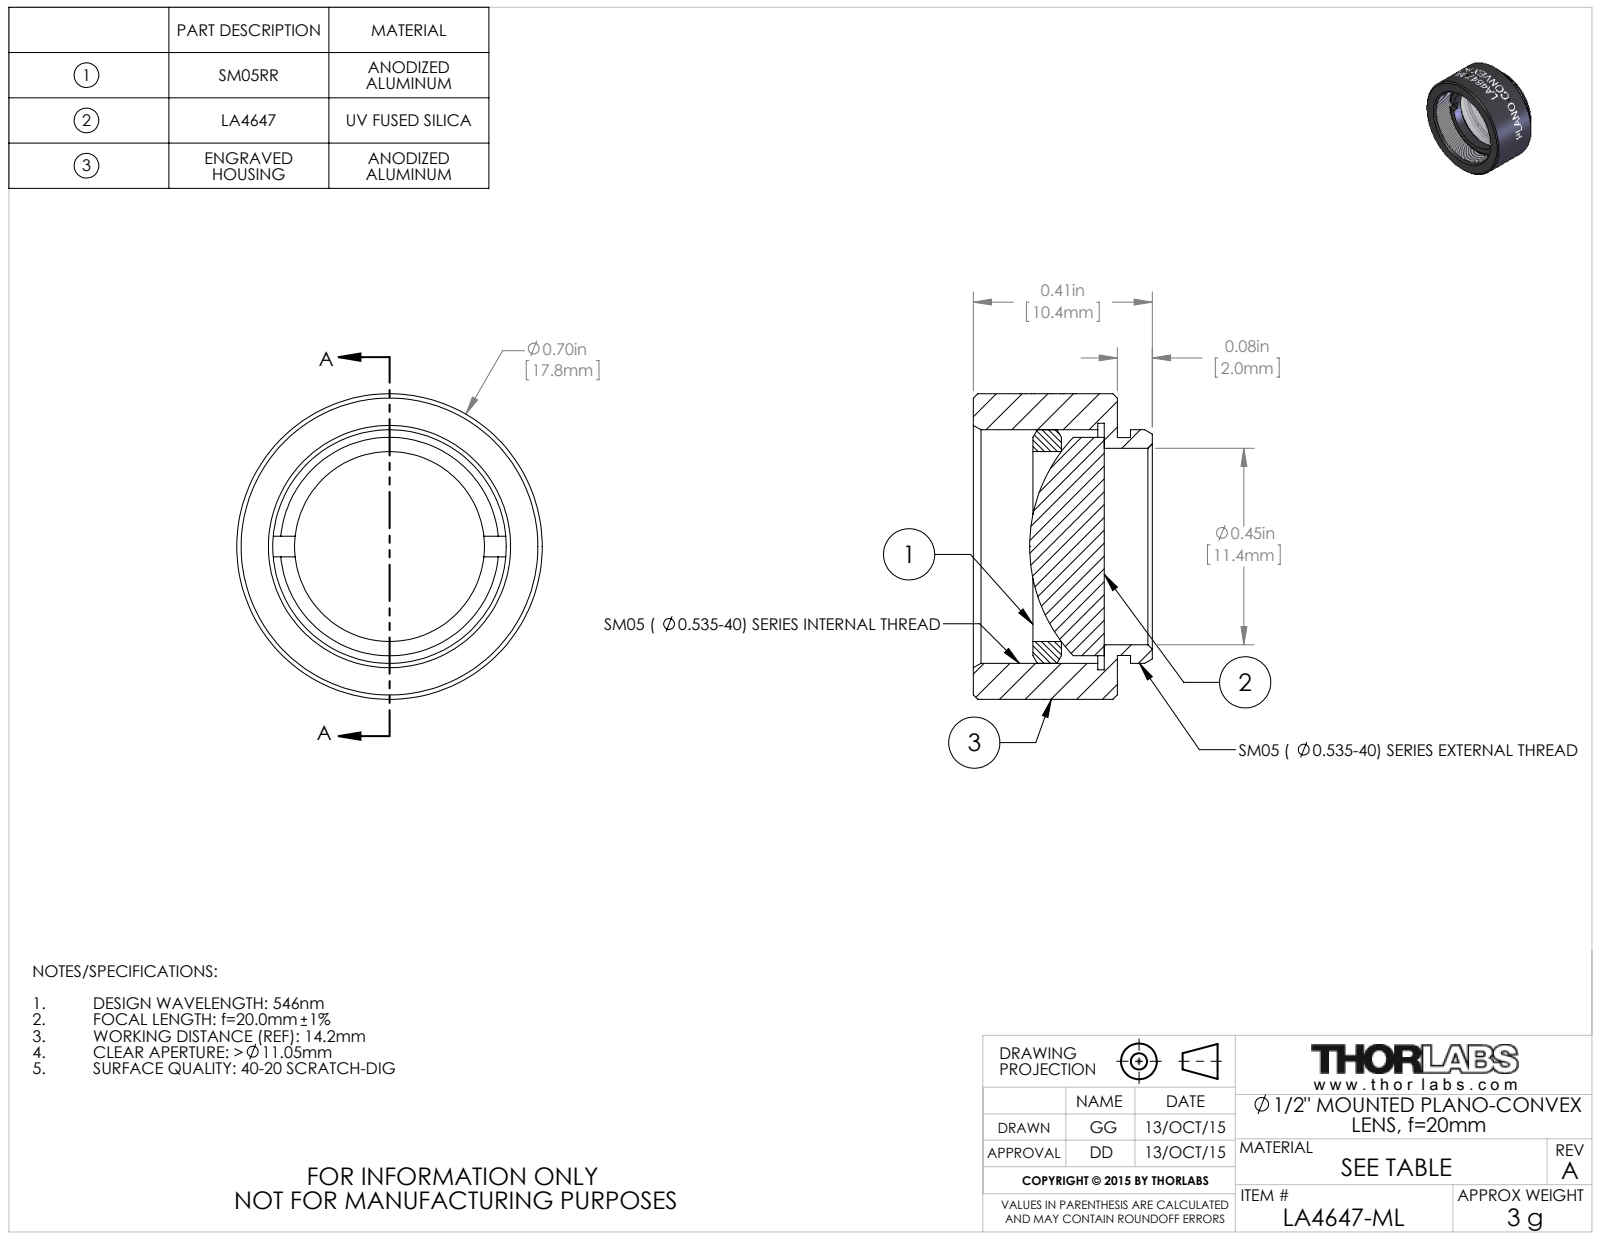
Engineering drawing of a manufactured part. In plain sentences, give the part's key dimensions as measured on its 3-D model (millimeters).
The part is named "TTN039330-E0W". Its 3-D file was written by "SolidWorks 2014 (CONFIG_CONTROL_DESIGN)". It is 3 solids with 107 faces: 16 planar, 74 cylindrical and 17 other. Overall it measures 17.78 by 17.78 by 10.41 millimeters. Its volume is 1 425 cubic millimeters and its surface area 1 860 square millimeters. Round holes: 1 of diameter 11.05, 1 of diameter 11.43, 1 of diameter 13.59, 1 of diameter 14.35. Round bosses or shafts: 1 of diameter 17.78, 1 of diameter 13.59, 1 of diameter 12.7, 1 of diameter 12.67. The main face-to-face distances are 0.76, 8.38, 7.62, 3.26, 2.5, 5.12, 4.91, 4.15, 1.65, 3.47.
